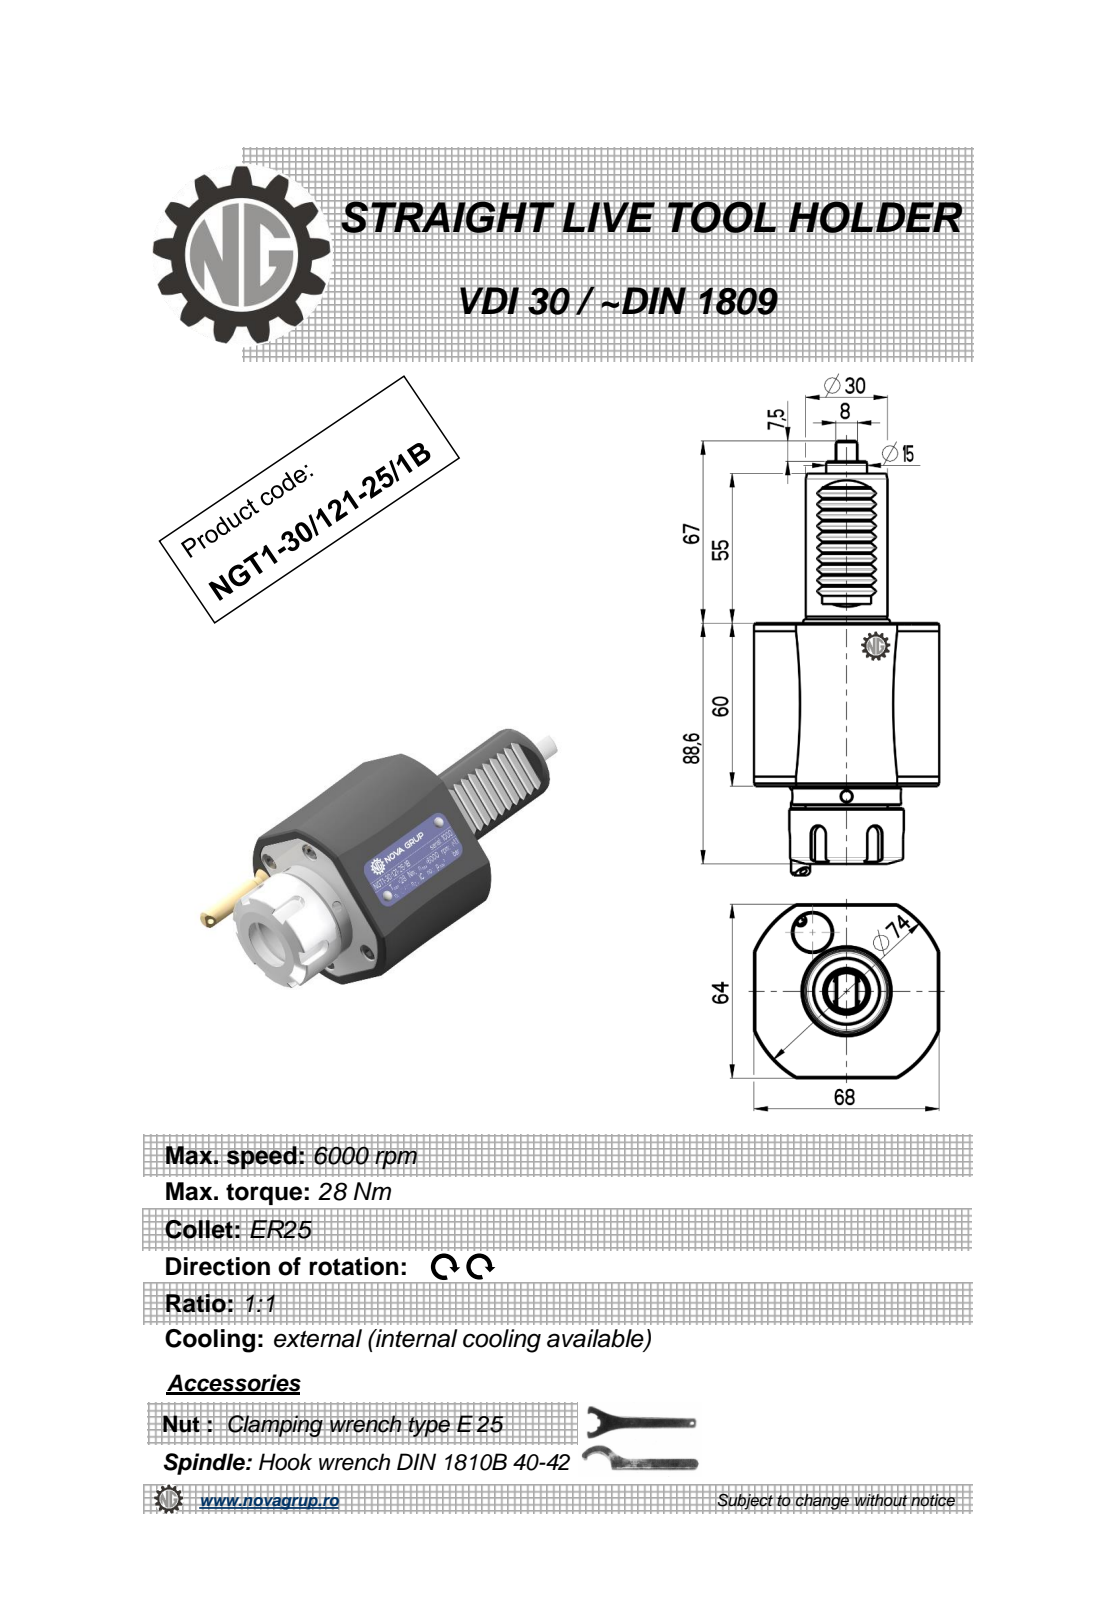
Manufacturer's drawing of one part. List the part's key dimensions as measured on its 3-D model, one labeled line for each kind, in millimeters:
Part name (STEP PRODUCT): NGT1_30_121_25_1B
STEP written by: PRO/ENGINEER BY PARAMETRIC TECHNOLOGY CORPORATION, 2010280 (CONFIG_CONTROL_DESIGN)
Units: millimetres
Bodies: 1 solid, 275 faces (111 planar, 68 cylindrical, 96 other)
Overall size (bounding box): 159.83 × 68 × 65.6
Volume: 305 404 mm³ · Surface area: 34 991 mm²
Round holes (diameter × count): ⌀4 ×2, ⌀2.5 ×1, ⌀3 ×1, ⌀20.3 ×1, ⌀25.8 ×1
Round bosses / shafts (diameter × count): ⌀42 ×1, ⌀40 ×1, ⌀33 ×1, ⌀30 ×1, ⌀15 ×1, ⌀9 ×1, ⌀7 ×1, ⌀5 ×1
Partial cylindrical surfaces — rounded edges, fillets, slot ends (radius × count): R0.3 ×10, R3 ×5, R0.8 ×2, R7.2 ×1, R13.9 ×1, R37 ×1
Main face-to-face distances: 60, 64, 68, 2.83, 81.7, 21.7, 67, 68.1, 8.1, 13.6
Hole centre spacings: 1.5, 29.75, 31
